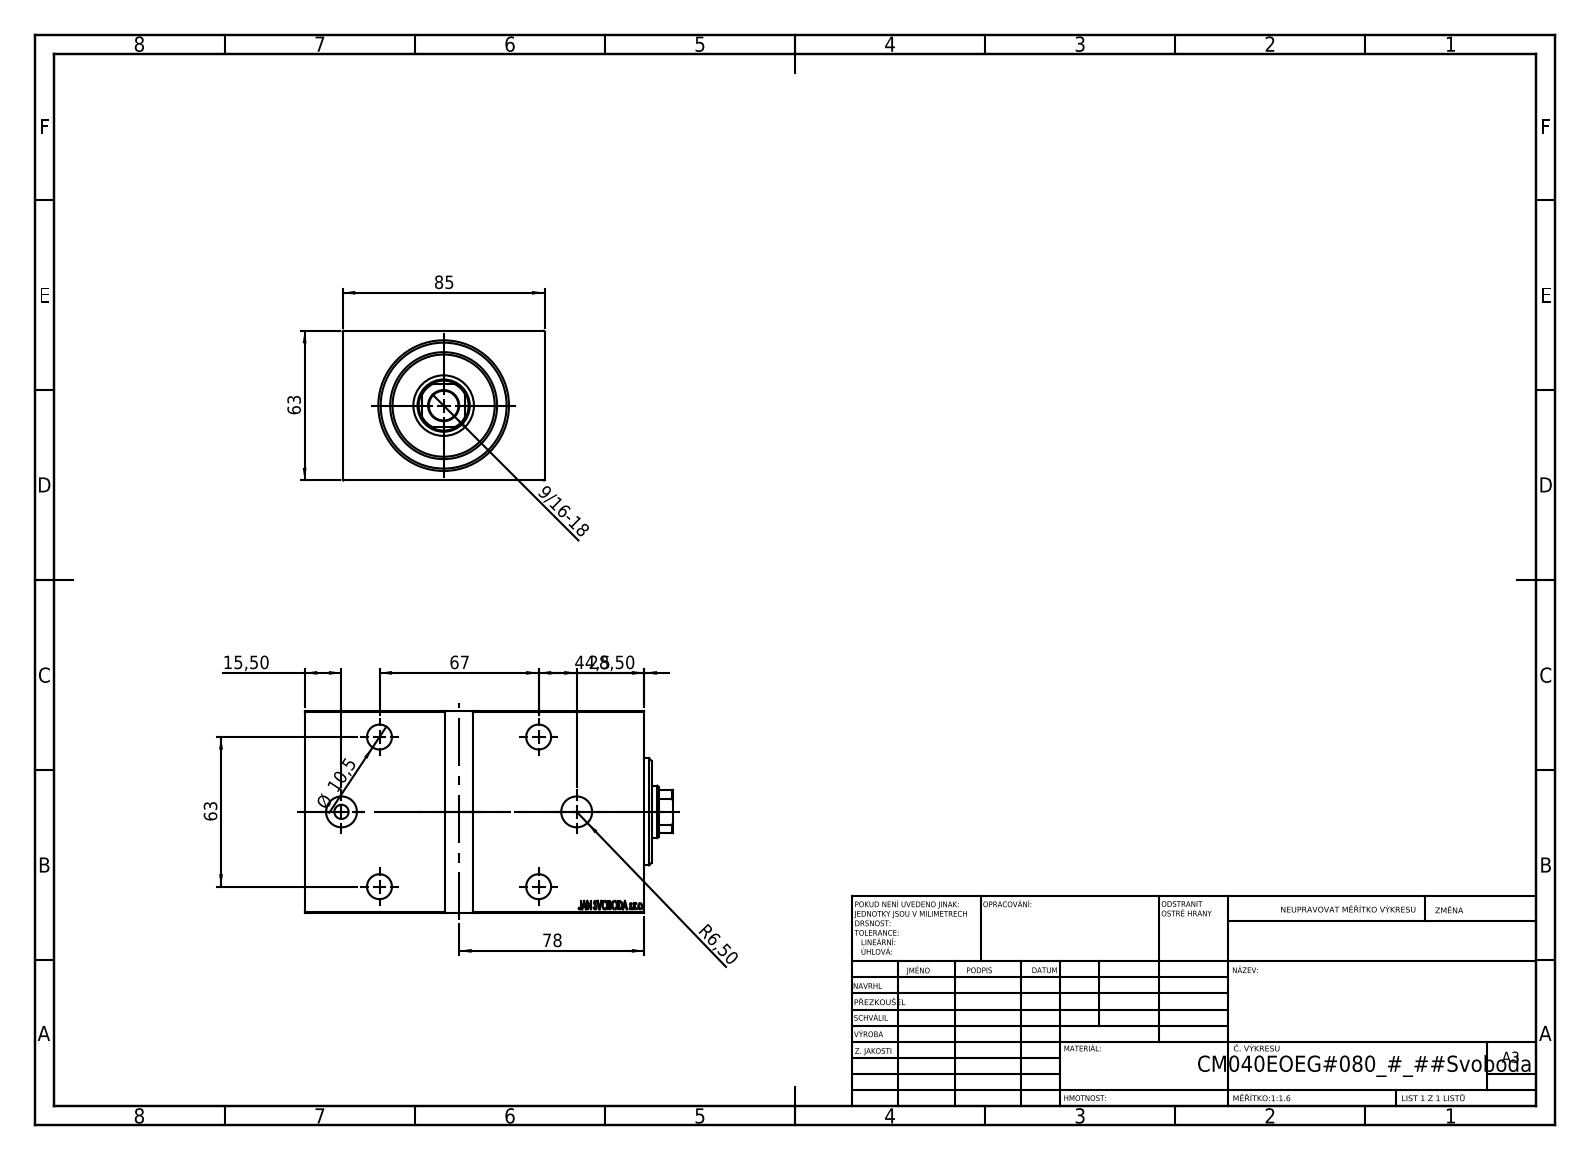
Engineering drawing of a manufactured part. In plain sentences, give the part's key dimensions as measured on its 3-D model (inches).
The part is named "V450CM_VC_B; V450CM_E_VCP; V450CM_E_Body". Its 3-D file was written by "SolidWorks 2019 (CONFIG_CONTROL_DESIGN)". It is 3 solids with 849 faces: 409 planar, 46 cylindrical and 394 other. Overall it measures 6.102 by 3.346 by 2.48 inches. Its volume is 41.02 cubic inches and its surface area 158.3 square inches. Round holes: 4 of diameter 0.413, 4 of diameter 0.65, 2 of diameter 0.512, 1 of diameter 0.492, 1 of diameter 0.866, 1 of diameter 1.004, 1 of diameter 1.575, 1 of diameter 2.087. Round bosses or shafts: 1 of diameter 1.772, 1 of diameter 1.654, 1 of diameter 0.236. Partial cylindrical surfaces (rounded edges, fillets, slot ends): 1 of radius 0.413. The main face-to-face distances are 2.48, 3.346, 5.63, 0.472, 5.157, 0.118, 0.197, 5.433, 4.961, 0.315. The hole center spacings are 1.391, 3.495, 2.48, 2.638, 3.621, 3.898.
